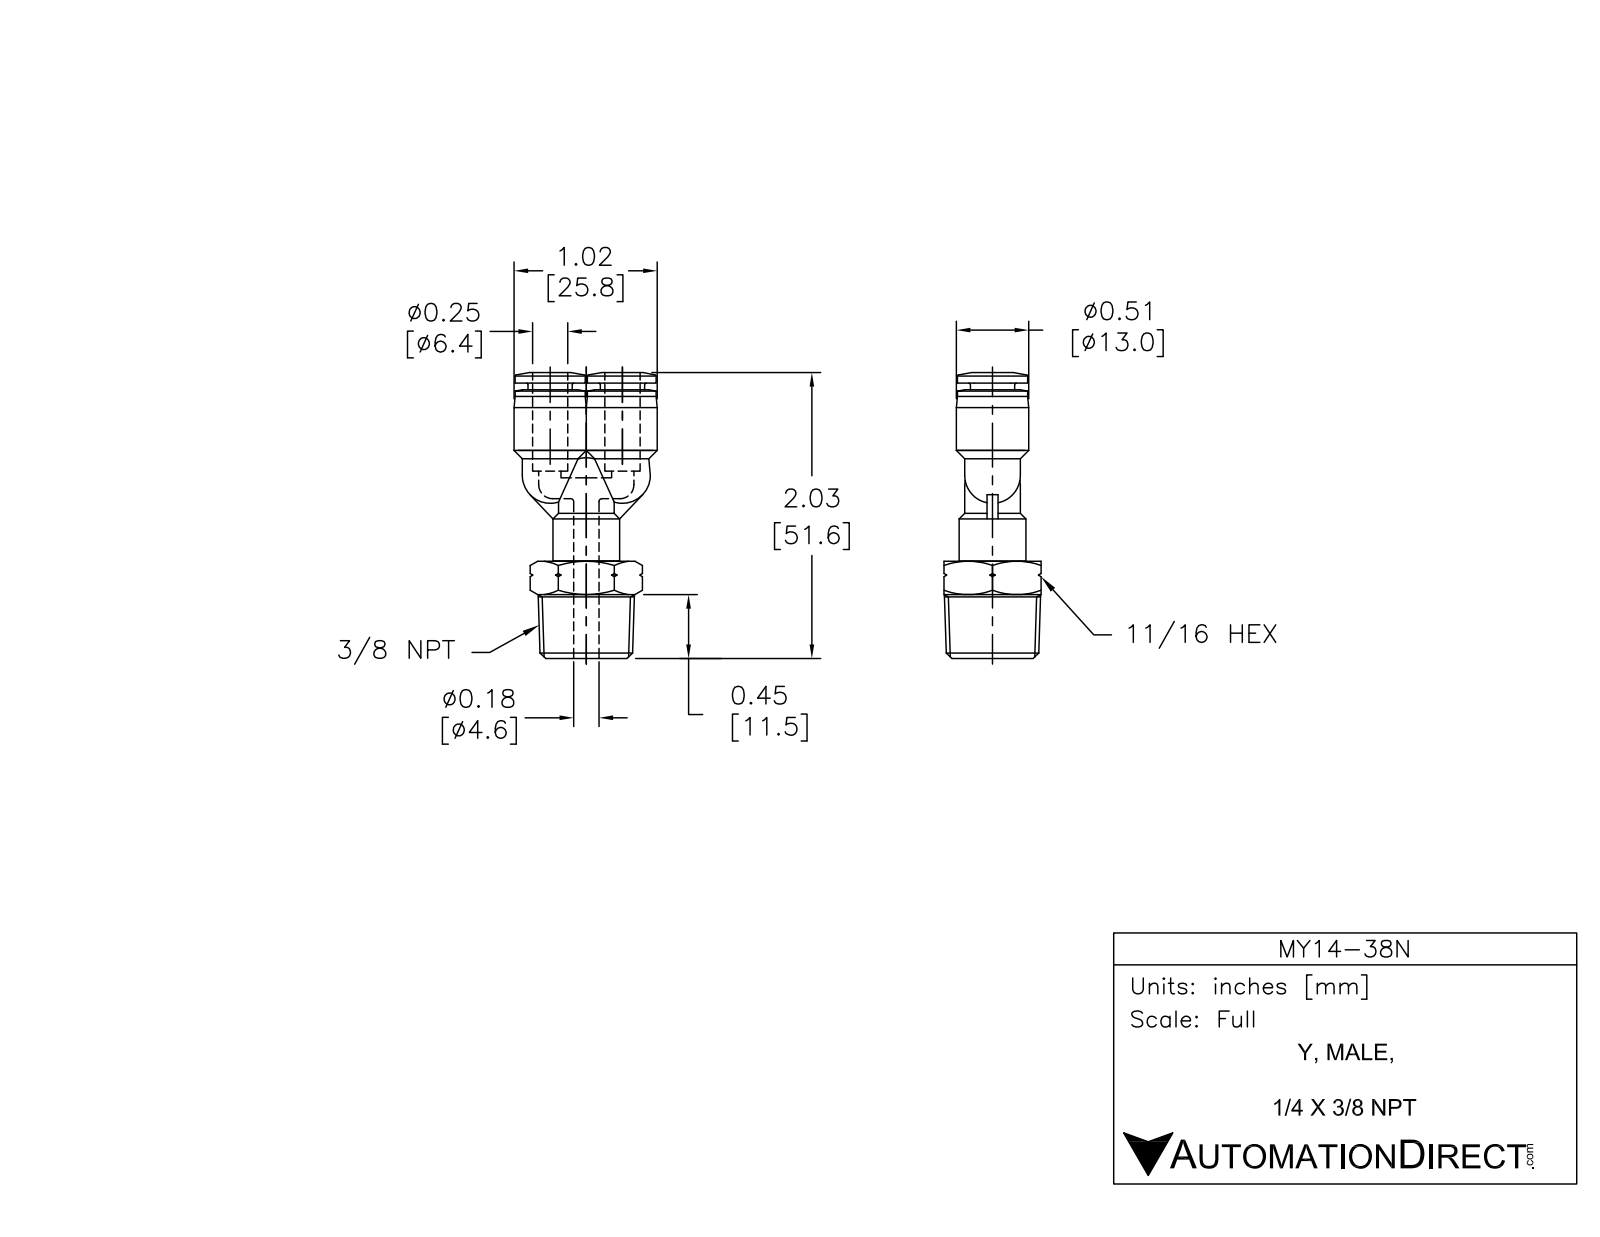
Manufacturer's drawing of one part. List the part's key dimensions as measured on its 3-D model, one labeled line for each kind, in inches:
Part name (STEP PRODUCT): MY14-38N
STEP written by: SolidWorks 2015 (AUTOMOTIVE_DESIGN)
Units: inches
Bodies: 1 solid, 126 faces (22 planar, 29 cylindrical, 75 other)
Overall size (bounding box): 2.024 × 1.024 × 0.687
Volume: 0.519 in³ · Surface area: 8.08 in²
Round holes (diameter × count): ⌀0.258 ×2, ⌀0.177 ×1
Round bosses / shafts (diameter × count): ⌀0.394 ×3, ⌀0.512 ×2, ⌀0.496 ×2, ⌀0.313 ×2, ⌀0.472 ×1
Main face-to-face distances: 0.687, 1.949, 0.689, 1.26, 0.63, 0.047, 1.902, 1.213, 0.304, 0.383
Hole centre spacings: 0.256, 0.512
